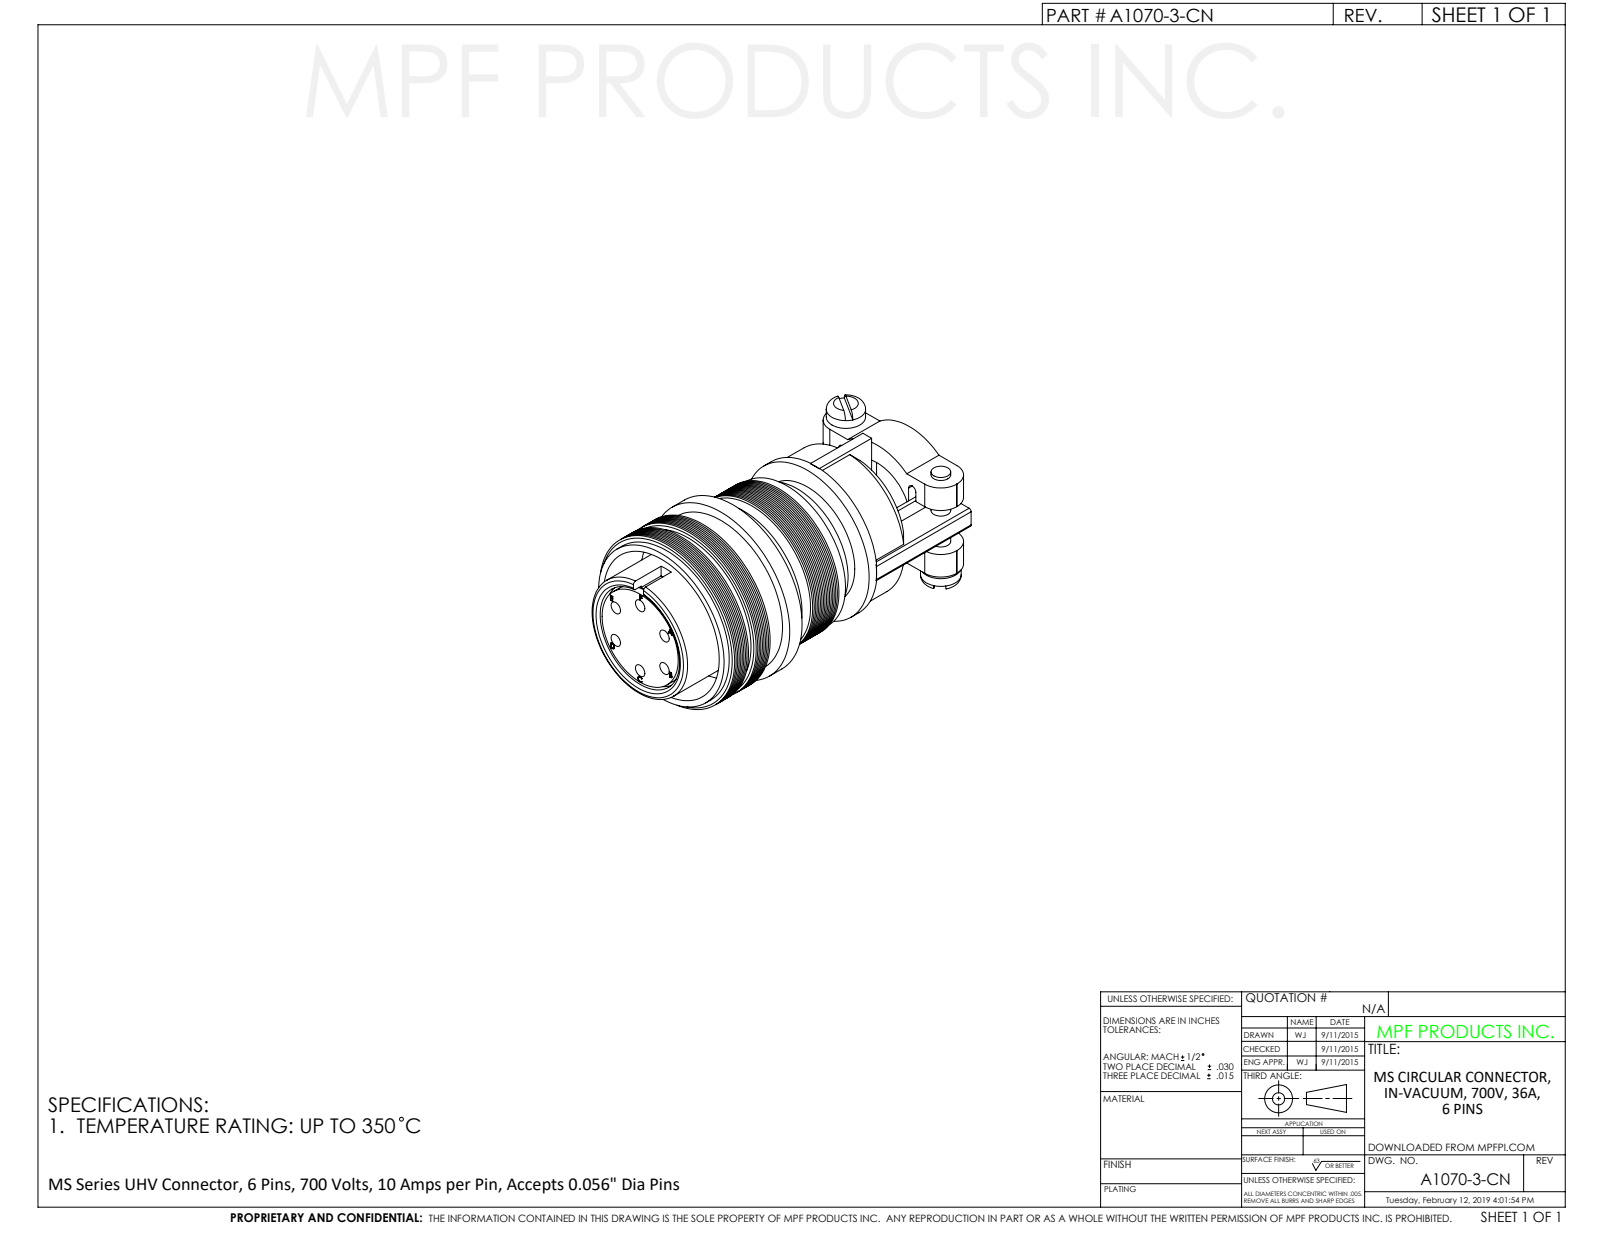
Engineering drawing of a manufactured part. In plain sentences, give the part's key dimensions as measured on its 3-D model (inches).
The part is named "A1070-3-CN". Its 3-D file was written by "SolidWorks 2012 (CONFIG_CONTROL_DESIGN)". It is 1 solid with 380 faces: 107 planar, 91 cylindrical and 182 other. Overall it measures 2.637 by 1.34 by 1.34 inches. Its volume is 2.227 cubic inches and its surface area 23.13 square inches. Round holes: 6 of diameter 0.091, 1 of diameter 0.646, 1 of diameter 0.78, 1 of diameter 1.125. Round bosses or shafts: 2 of diameter 0.135, 1 of diameter 1.34, 1 of diameter 1.223, 1 of diameter 1.22, 1 of diameter 1.2, 1 of diameter 1.14, 1 of diameter 0.99, 1 of diameter 0.92. Partial cylindrical surfaces (rounded edges, fillets, slot ends): 8 of radius 0.034, 4 of radius 0.02, 4 of radius 0.156, 1 of radius 0.472, 1 of radius 0.473. The main face-to-face distances are 1.193, 0.643, 0.47, 0.722, 0.1, 0.2, 0.522, 0.992, 1.714, 2.618. The hole center spacings are 0.273, 0.473, 0.546.
